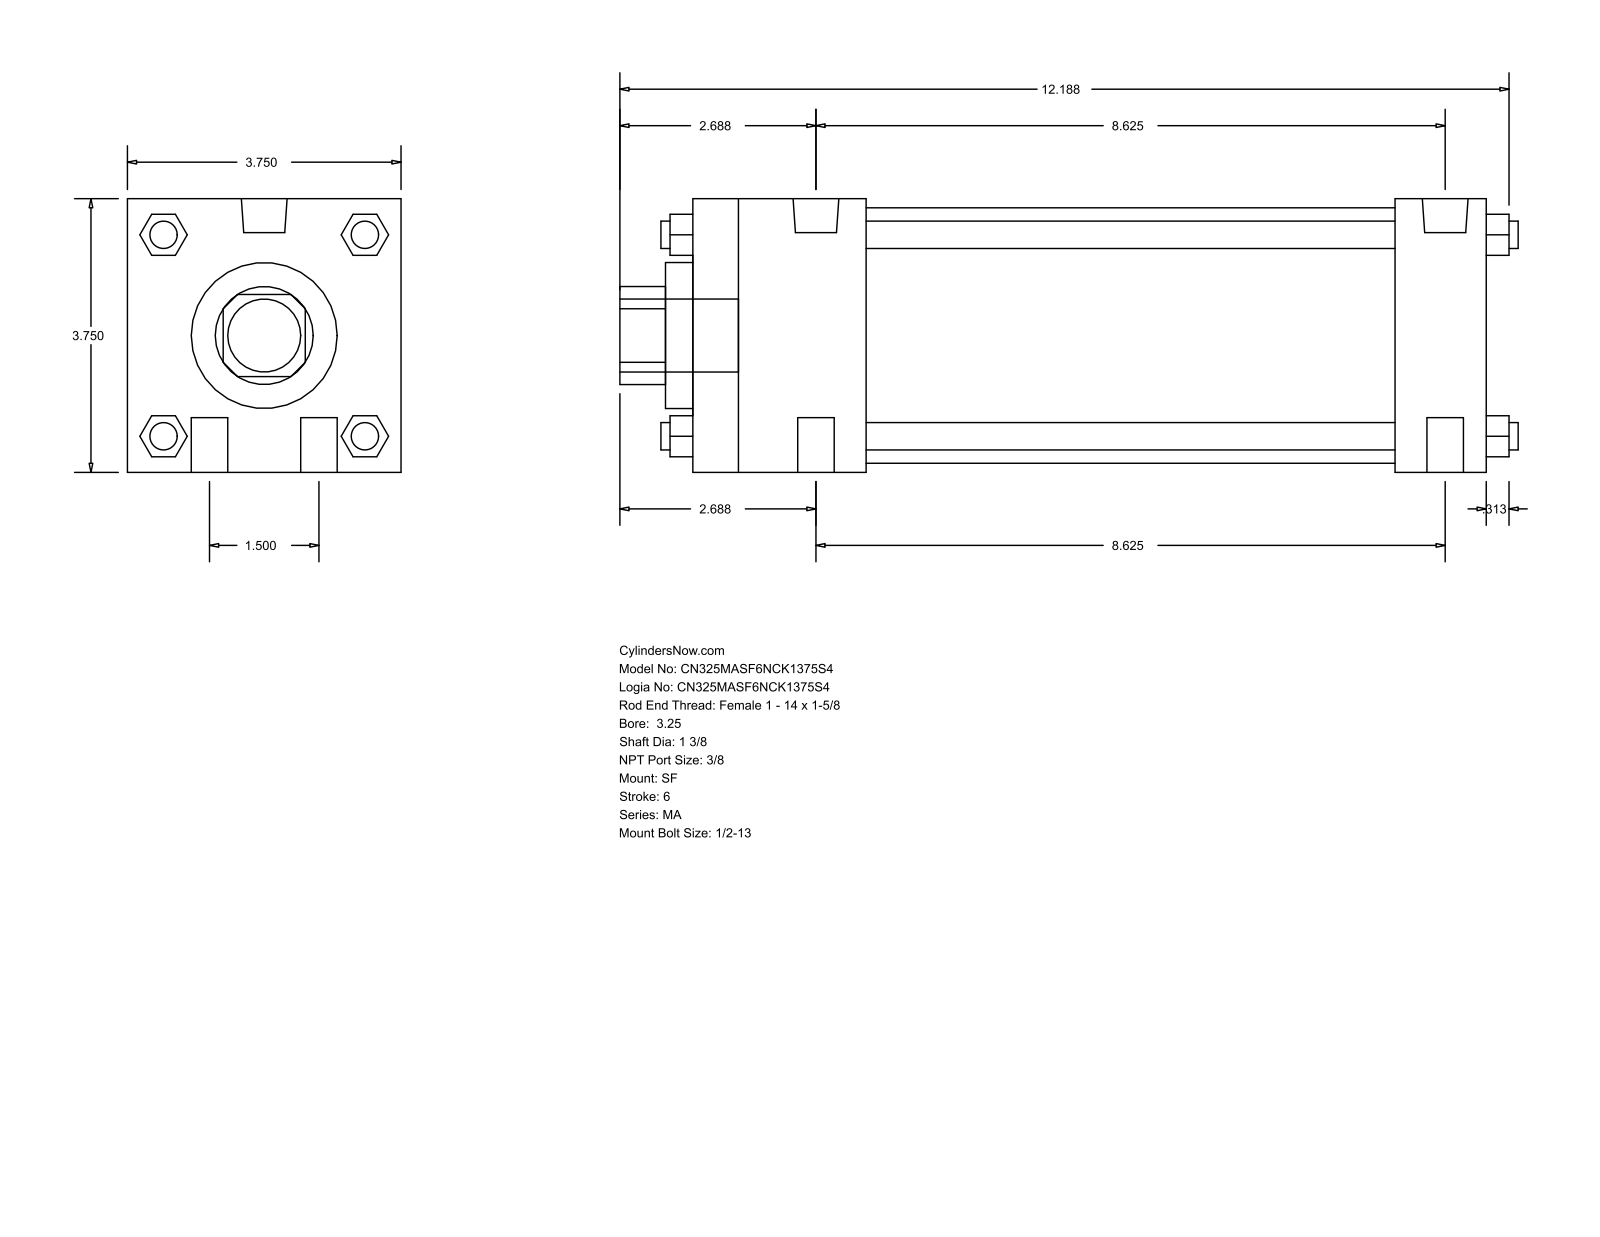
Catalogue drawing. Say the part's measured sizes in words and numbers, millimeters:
The part is named "MA_SF__0325_1.375". Its 3-D file was written by "GSSL Pune (CONFIG_CONTROL_DESIGN)". It is 0 solids with 124 faces: 94 planar, 30 cylindrical and 0 other. Overall it measures 312.74 by 95.25 by 95.25 millimeters. Round holes: 1 of diameter 34.92, 1 of diameter 50.8, 1 of diameter 88.9. Round bosses or shafts: 4 of diameter 12.7, 4 of diameter 9.53, 2 of diameter 15.93, 2 of diameter 11.11, 1 of diameter 25.4. Partial cylindrical surfaces (rounded edges, fillets, slot ends): 1 of radius 17.06. The main face-to-face distances are 95.24, 276.22, 244.48, 31.74, 60.32, 184.16, 215.9, 9.52, 69.84, 254.
